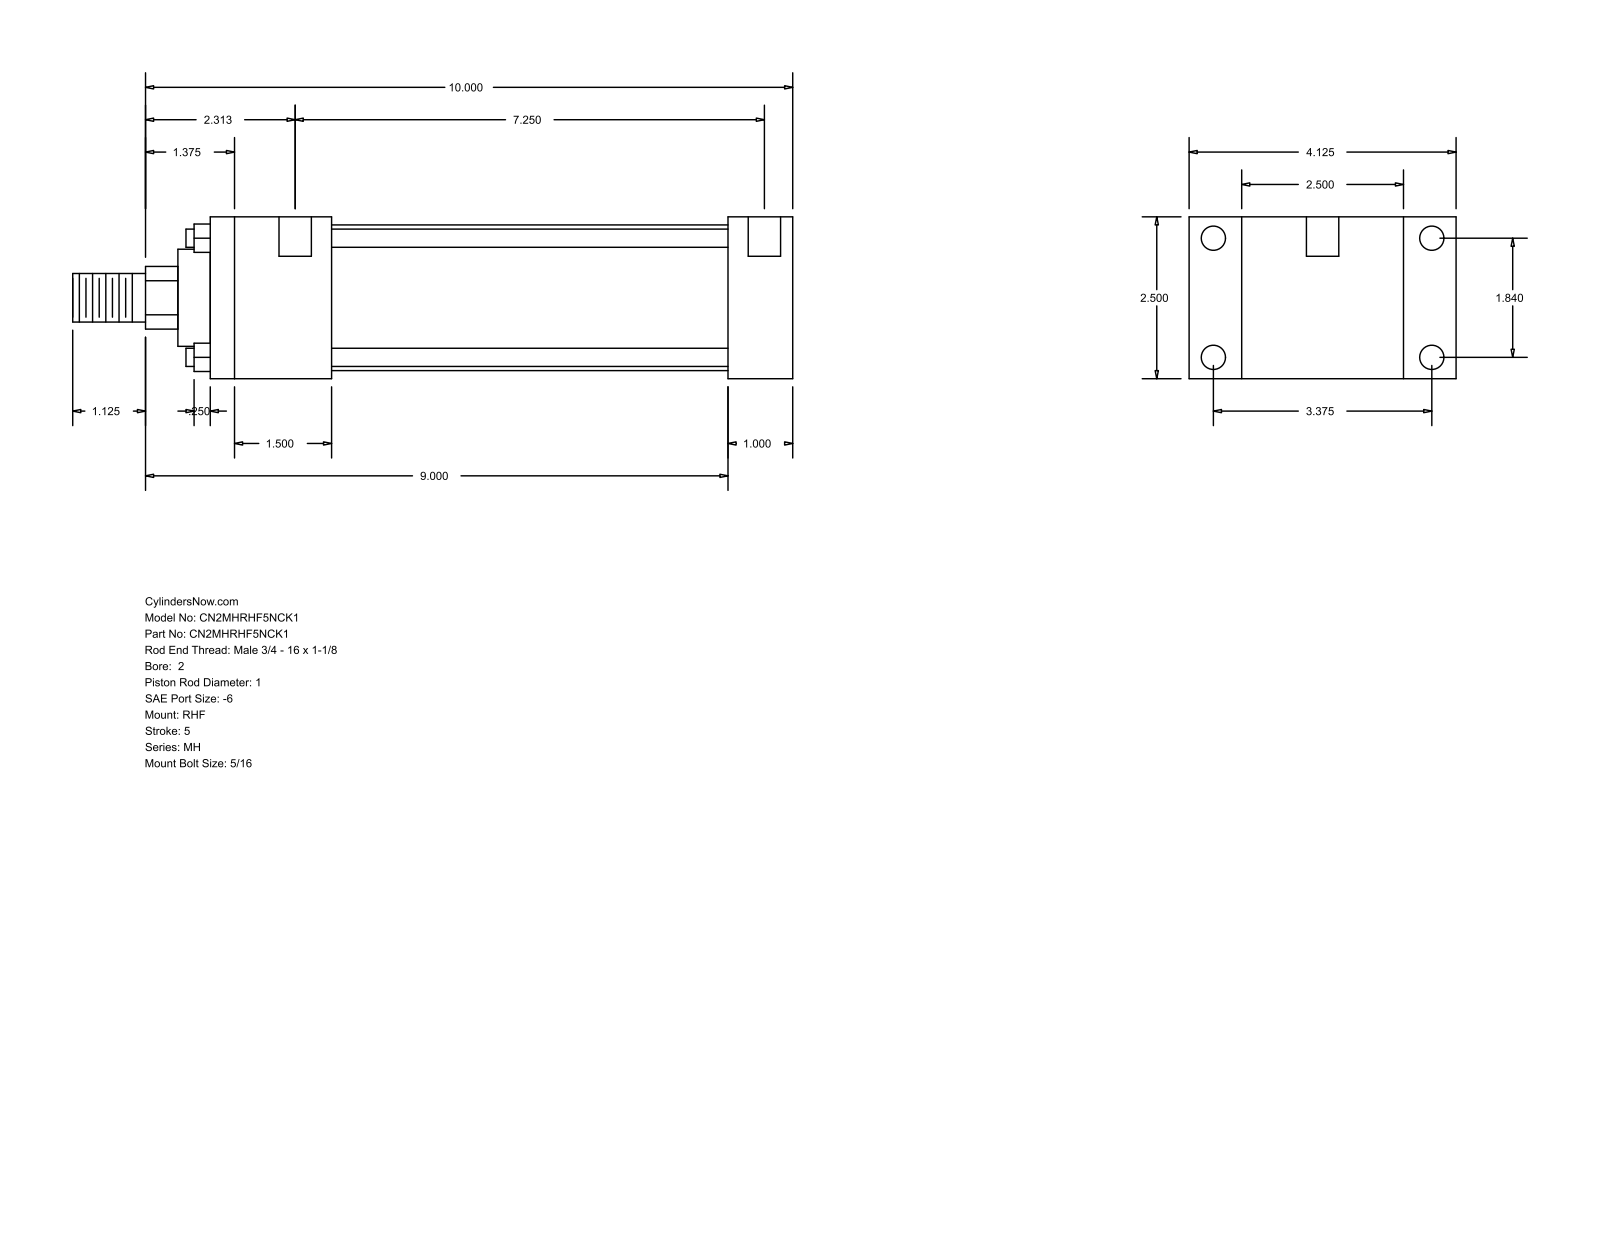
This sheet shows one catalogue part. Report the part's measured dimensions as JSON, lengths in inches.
{"part_name": "MH_RHF__0200_1", "step_written_by": "GSSL Pune (CONFIG_CONTROL_DESIGN)", "units": "inches", "bodies": {"solids": 0, "faces": 88, "planar": 60, "cylindrical": 28, "other": 0}, "overall_size": [11.125, 4.125, 2.5], "round_holes": [[0.219, 4], [0.375, 4], [0.5, 2]], "round_bosses_or_shafts": [[0.281, 4], [2.25, 1], [1.5, 1], [1, 1], [0.75, 1]], "partial_cylinders_radius": [[0.484, 1]], "face_to_face_distances": [2.5, 1, 0.813, 3.313, 9, 8, 4.125, 1.875, 6.125, 7.125], "hole_center_spacings": [1.84, 3.375, 3.844, 7.562, 0.125, 0.187, 7.25, 7.375]}
